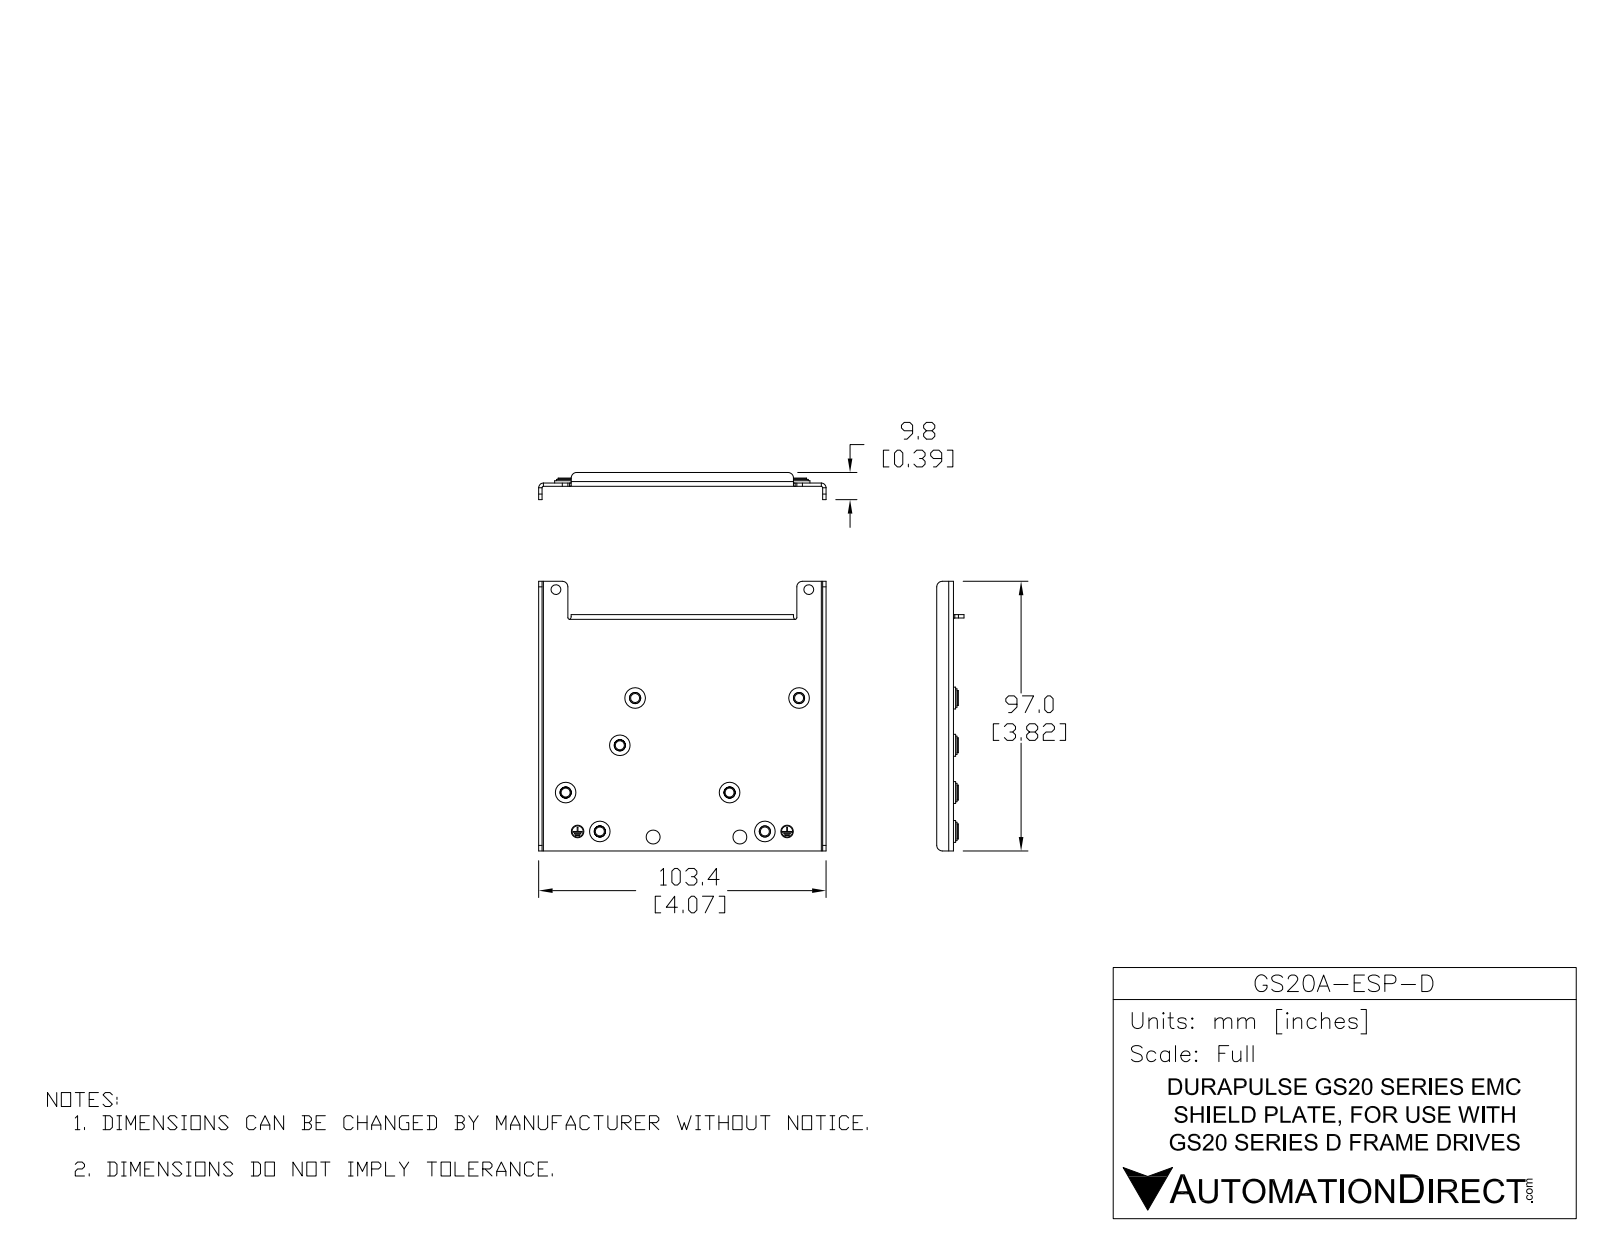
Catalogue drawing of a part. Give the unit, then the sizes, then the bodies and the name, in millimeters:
Units: millimetres
Overall size (bounding box): 103.4 × 97 × 29.1
Round holes (diameter × count): ⌀3.3 ×7, ⌀5.4 ×7, ⌀5.4 ×5, ⌀3.5 ×2, ⌀5 ×2, ⌀8 ×2
Round bosses / shafts (diameter × count): ⌀7.9 ×7, ⌀5.4 ×7, ⌀6.6 ×4, ⌀6.6 ×3, ⌀8 ×2, ⌀7.2 ×2, ⌀6.9 ×2, ⌀4 ×2
Partial cylindrical surfaces — rounded edges, fillets, slot ends (radius × count): R2.7 ×10, R7.5 ×10, R0.5 ×8, R2 ×6, R7 ×5, R8 ×5, R1.7 ×3
Main face-to-face distances: 1.2, 1, 2.2, 29.5, 102.2, 28.5, 30.5, 9.8, 19.8, 2
Hole centre spacings: 9, 42.2, 59, 68.4, 87.3, 88.4, 115, 121.1
Volume: 19 420 mm³ · Surface area: 36 260 mm²
Bodies: 15 solids, 586 faces (232 planar, 159 cylindrical, 195 other)
Part name (STEP PRODUCT): MKM-EPD-PD-3D00 r1
STEP written by: SolidWorks 2017 (AUTOMOTIVE_DESIGN)
